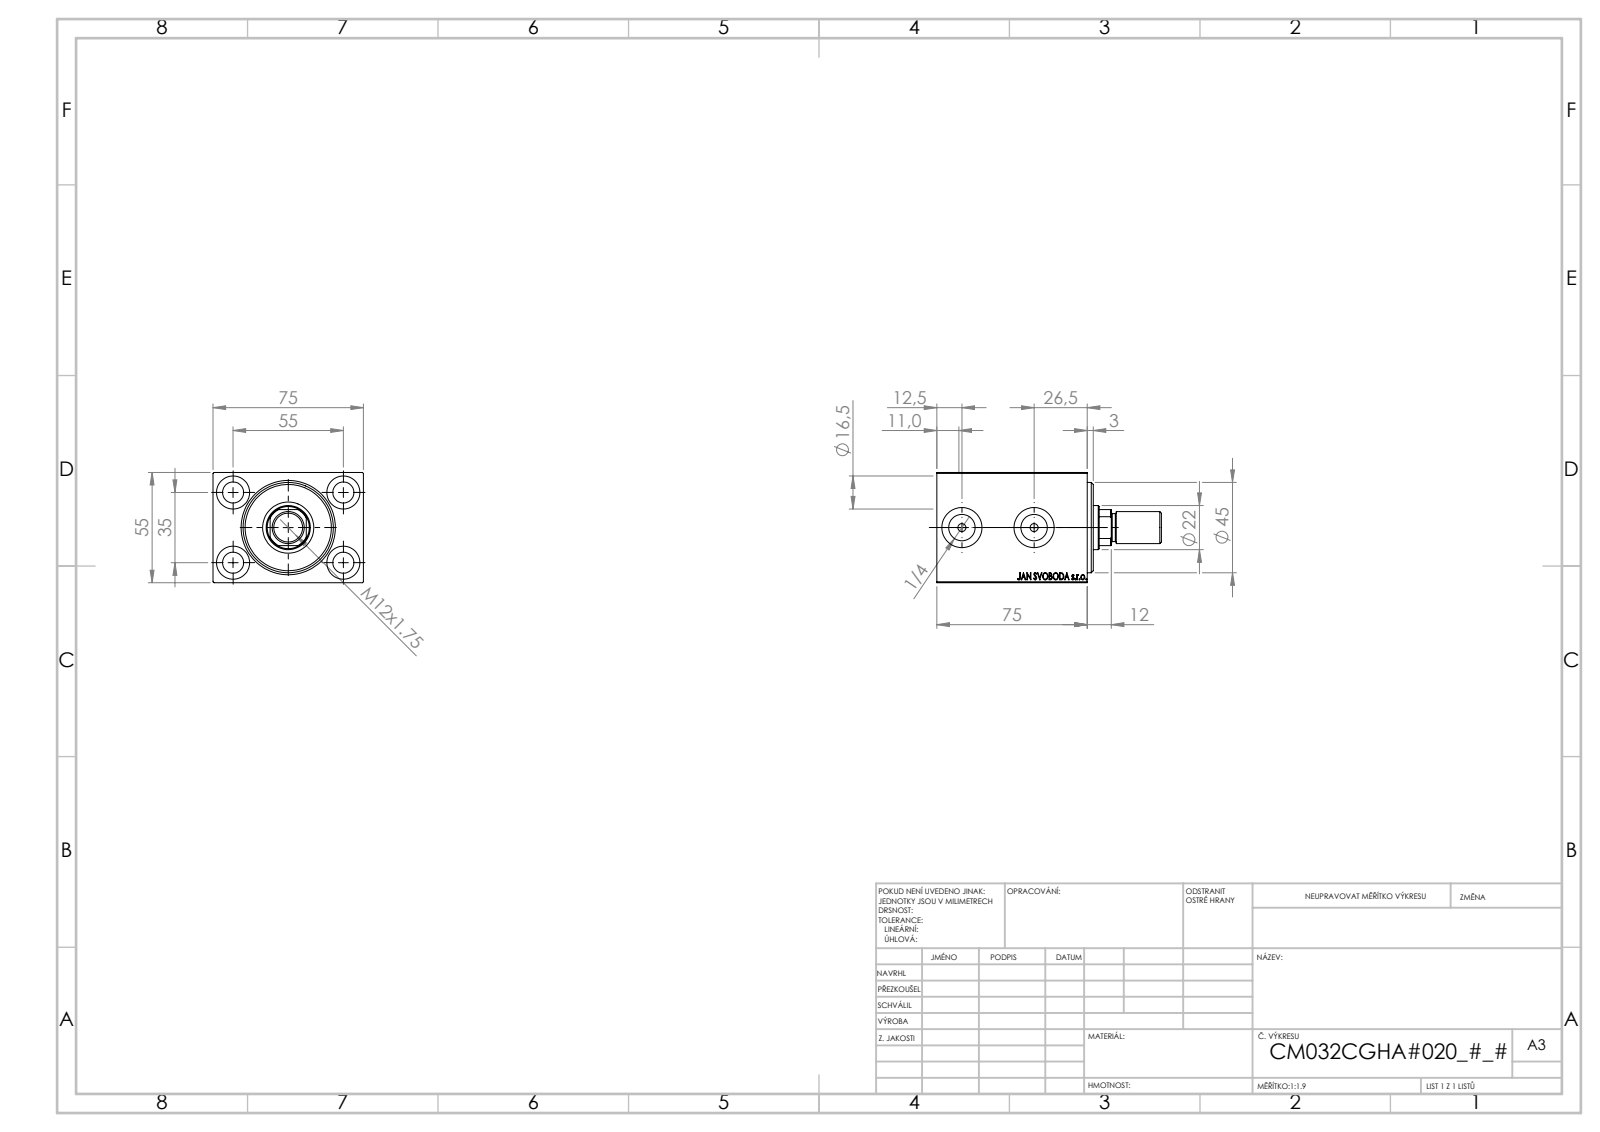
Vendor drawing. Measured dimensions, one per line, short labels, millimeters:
name: V450CM_C_VCP; V450CM_C_Body; V450CM_MALE_METRIC; V450CM_VC_B
written by: SolidWorks 2019 (CONFIG_CONTROL_DESIGN)
unit: mm
bodies: 4 solids, 875 faces (411 planar, 64 cylindrical, 400 other)
size: 112 × 75 × 55
volume: 270 589 mm³; area: 63 908 mm²
holes: 5× ⌀10.5, 4× ⌀16.5, 2× ⌀4, 2× ⌀13.16, 2× ⌀20, 1× ⌀22, 1× ⌀25.5, 1× ⌀32, 1× ⌀34, 1× ⌀45
bosses: 1× ⌀16, 1× ⌀14
rounds: 1× R10.5
face distances: 55, 75, 10, 65, 70, 5, 60, 11, 64, 3
hole spacings: 32.6, 35, 55, 65.19, 36
